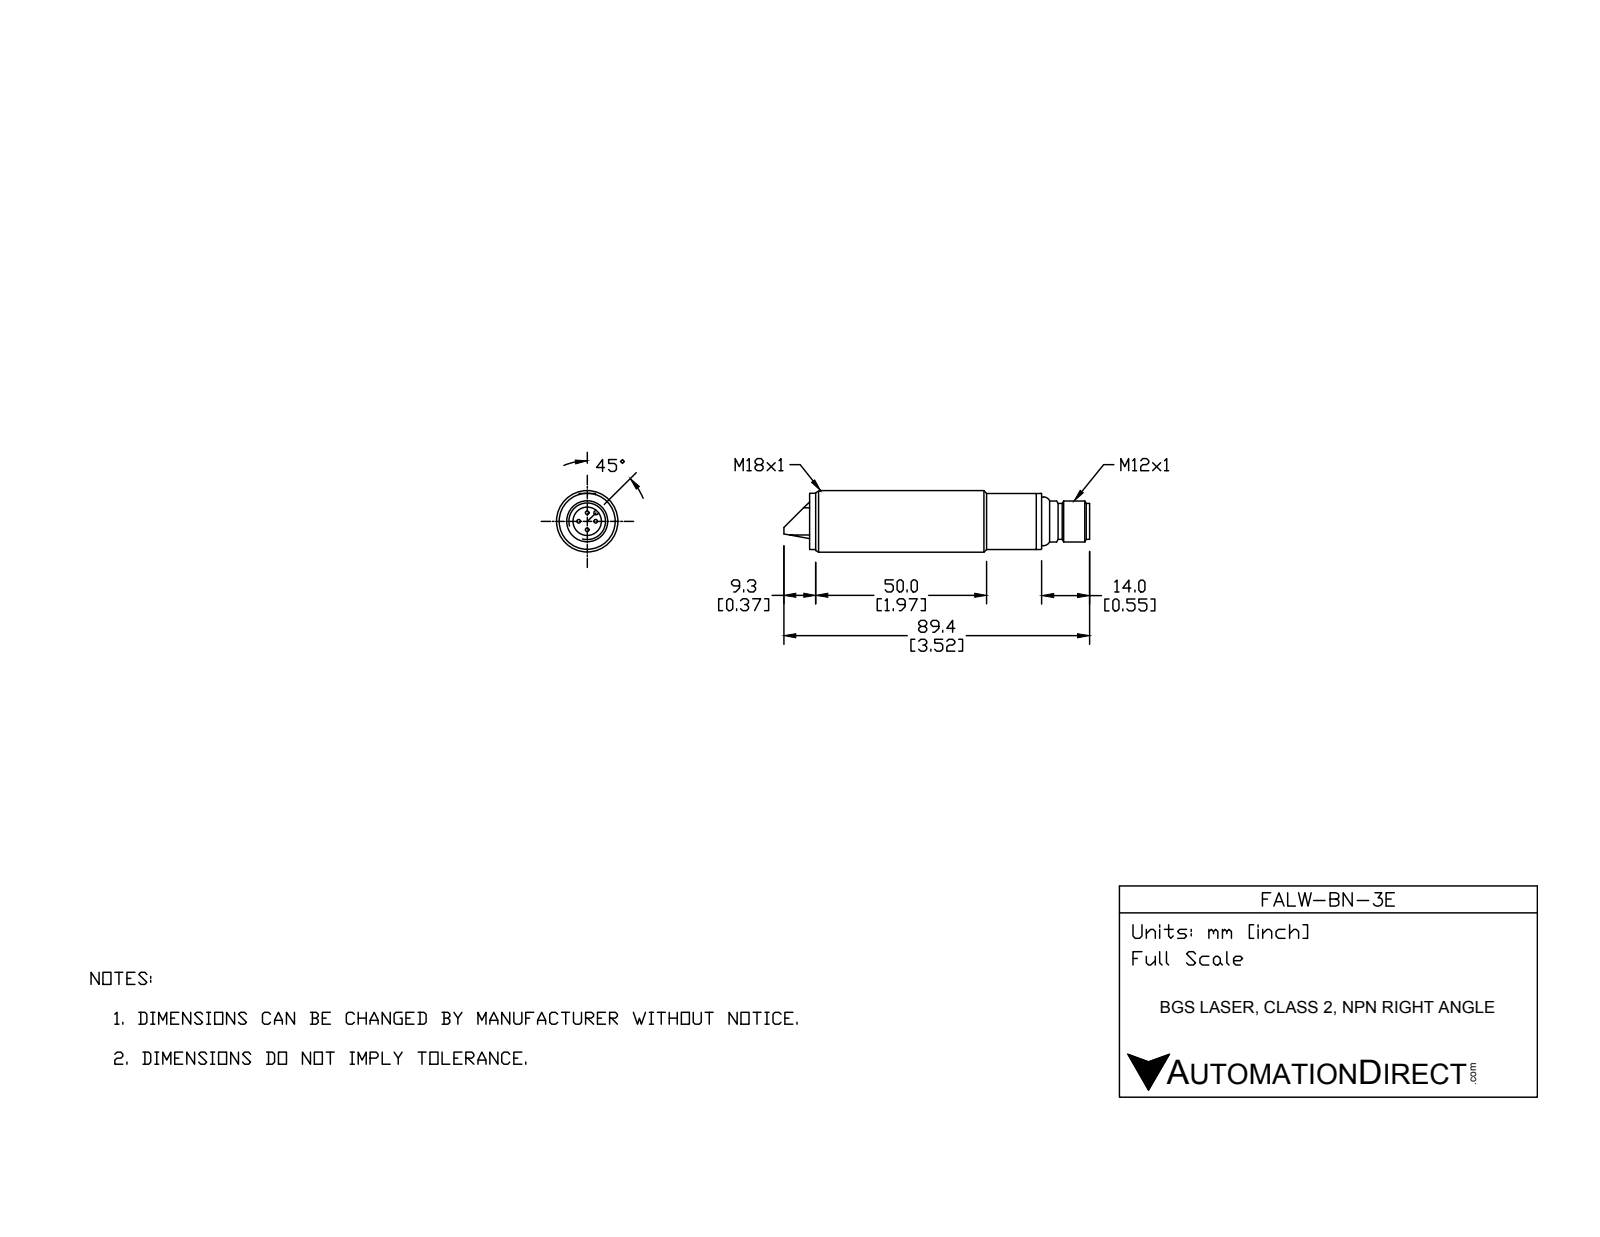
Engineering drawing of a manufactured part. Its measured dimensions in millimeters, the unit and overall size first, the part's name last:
Units: millimetres
Overall size (bounding box): 89.4 × 18 × 18
Round holes (diameter × count): ⌀1 ×4, ⌀1.1 ×4, ⌀2.7 ×1, ⌀4.7 ×1, ⌀7.1 ×1, ⌀8.3 ×1, ⌀15 ×1, ⌀15.8 ×1
Round bosses / shafts (diameter × count): ⌀18 ×1, ⌀16.5 ×1, ⌀16.4 ×1, ⌀14.2 ×1, ⌀12 ×1, ⌀10.5 ×1, ⌀7 ×1, ⌀4.8 ×1
Partial cylindrical surfaces — rounded edges, fillets, slot ends (radius × count): R0.5 ×4, R0.6 ×1, R8.1 ×1, R8.4 ×1
Main face-to-face distances: 1, 64.3, 1.8, 1.4, 62.9, 0.4, 62.5, 2.4, 2.8, 65.3
Hole centre spacings: 2.5, 3.5, 5
Volume: 17 960 mm³ · Surface area: 7 323 mm²
Bodies: 11 solids, 189 faces (63 planar, 81 cylindrical, 45 other)
Part name (STEP PRODUCT): FALW-BN-3E
STEP written by: SolidWorks 2017 (AUTOMOTIVE_DESIGN)
